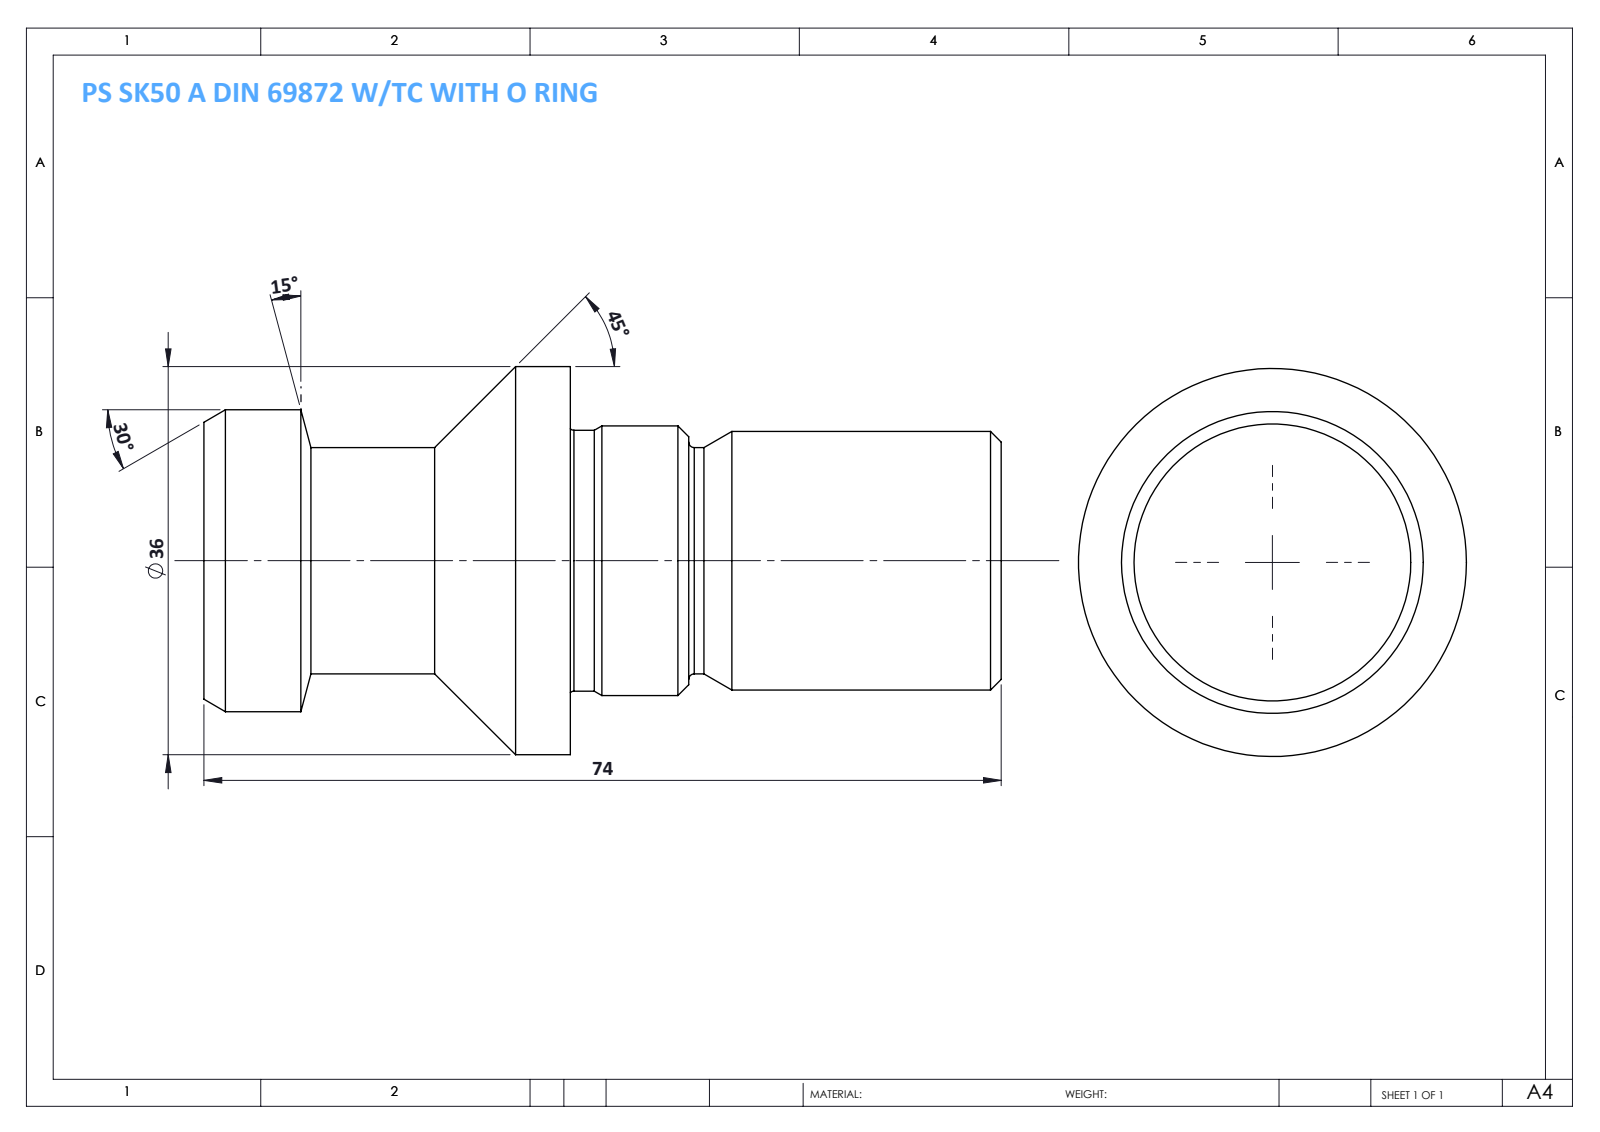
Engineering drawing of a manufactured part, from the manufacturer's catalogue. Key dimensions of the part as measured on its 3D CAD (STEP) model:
Part name (STEP PRODUCT): PS SK50 A DIN 69872 W-TC WITH O RING
STEP written by: SolidWorks 2014 (CONFIG_CONTROL_DESIGN)
Units: millimetres
Bodies: 1 solid, 38 faces (4 planar, 14 cylindrical, 20 other)
Overall size (bounding box): 74 × 36 × 36
Volume: 38 003 mm³ · Surface area: 7 990 mm²
Round bosses / shafts (diameter × count): ⌀36 ×1, ⌀28 ×1, ⌀25 ×1, ⌀24.2 ×1, ⌀24 ×1, ⌀21 ×1
Main face-to-face distances: 34, 40, 74, 29, 11, 45
